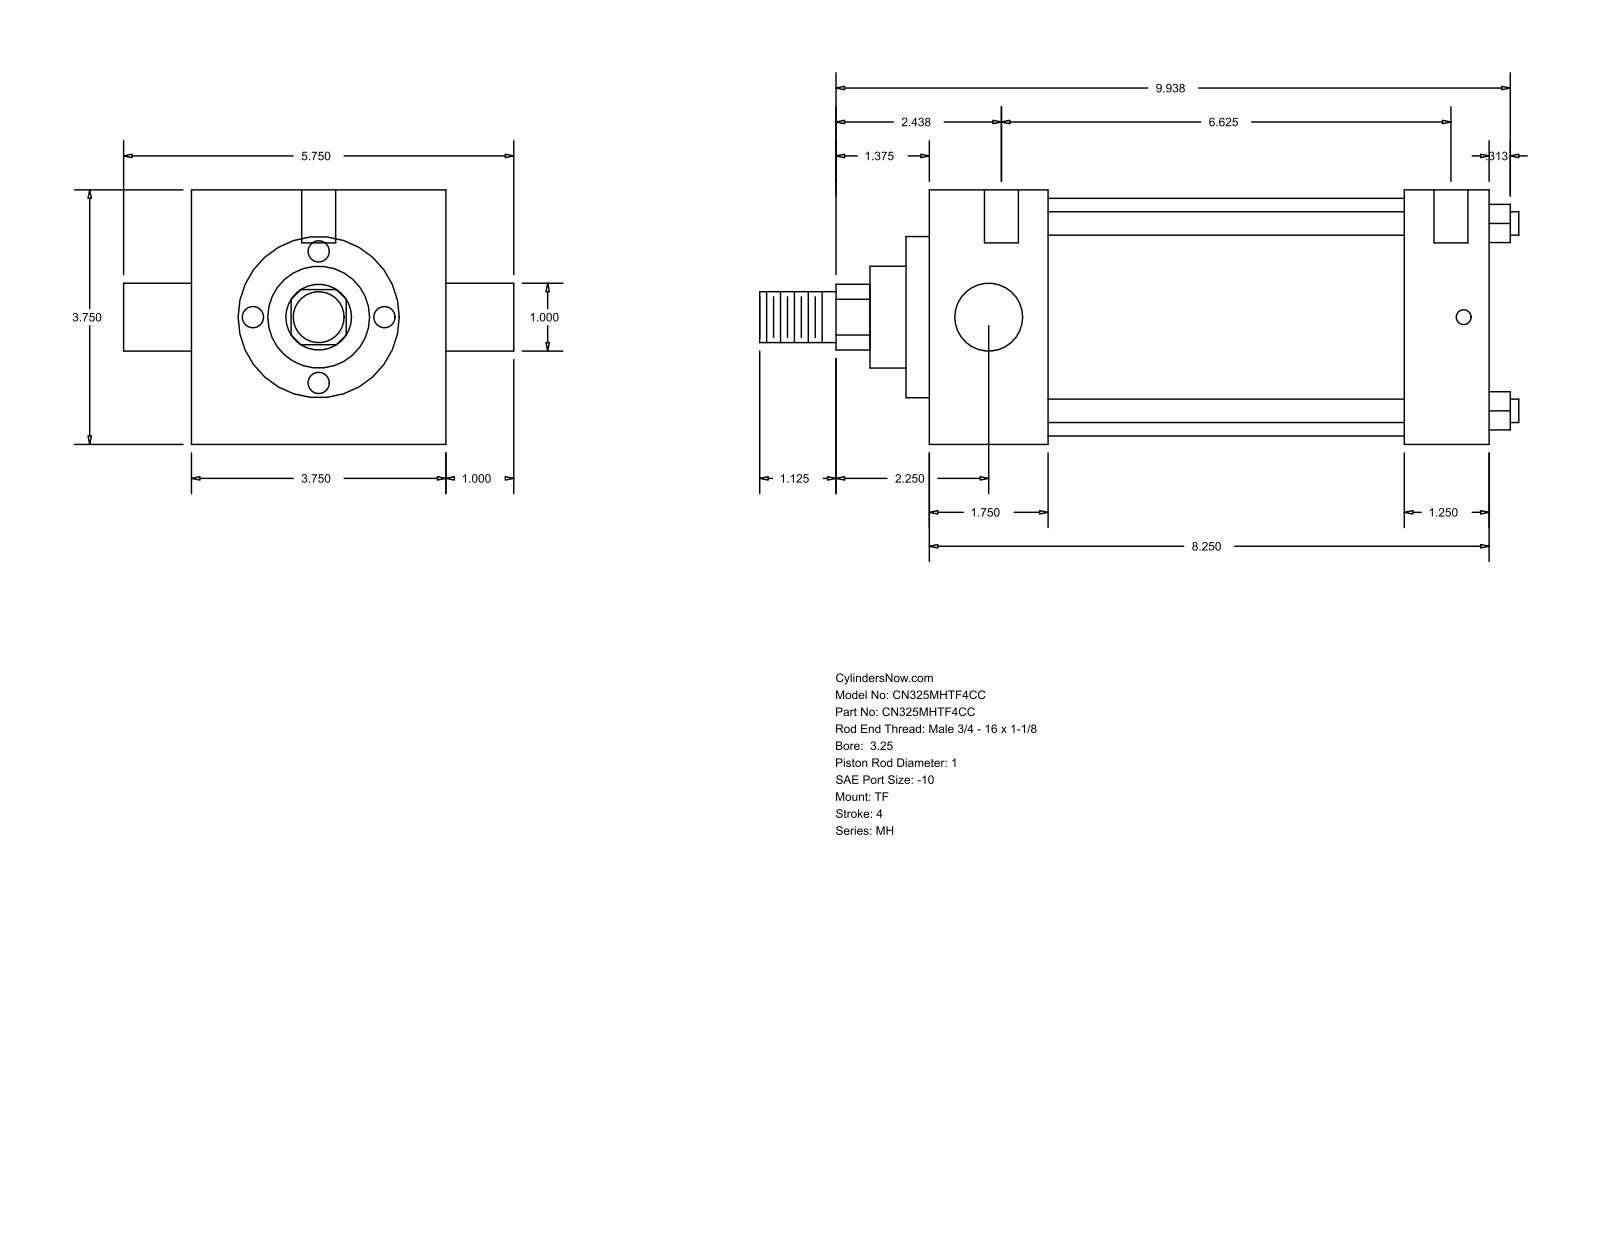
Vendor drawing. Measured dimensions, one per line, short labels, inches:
name: MH_TF__0325_1
written by: GSSL Pune (CONFIG_CONTROL_DESIGN)
unit: in
bodies: 0 solids, 86 faces (61 planar, 25 cylindrical, 0 other)
size: 11.187 × 5.75 × 3.75
holes: 3× ⌀0.219, 2× ⌀0.5
bosses: 4× ⌀0.345, 2× ⌀1, 1× ⌀3.5, 1× ⌀2.375, 1× ⌀1.5, 1× ⌀0.75
rounds: 1× R0.484
face distances: 3.75, 8.25, 1.75, 7, 5.25, 6.5, 1.25, 0.344, 2.094, 7.344
hole spacings: 0.062, 0.187, 6.625, 6.687, 6.813, 6.875
